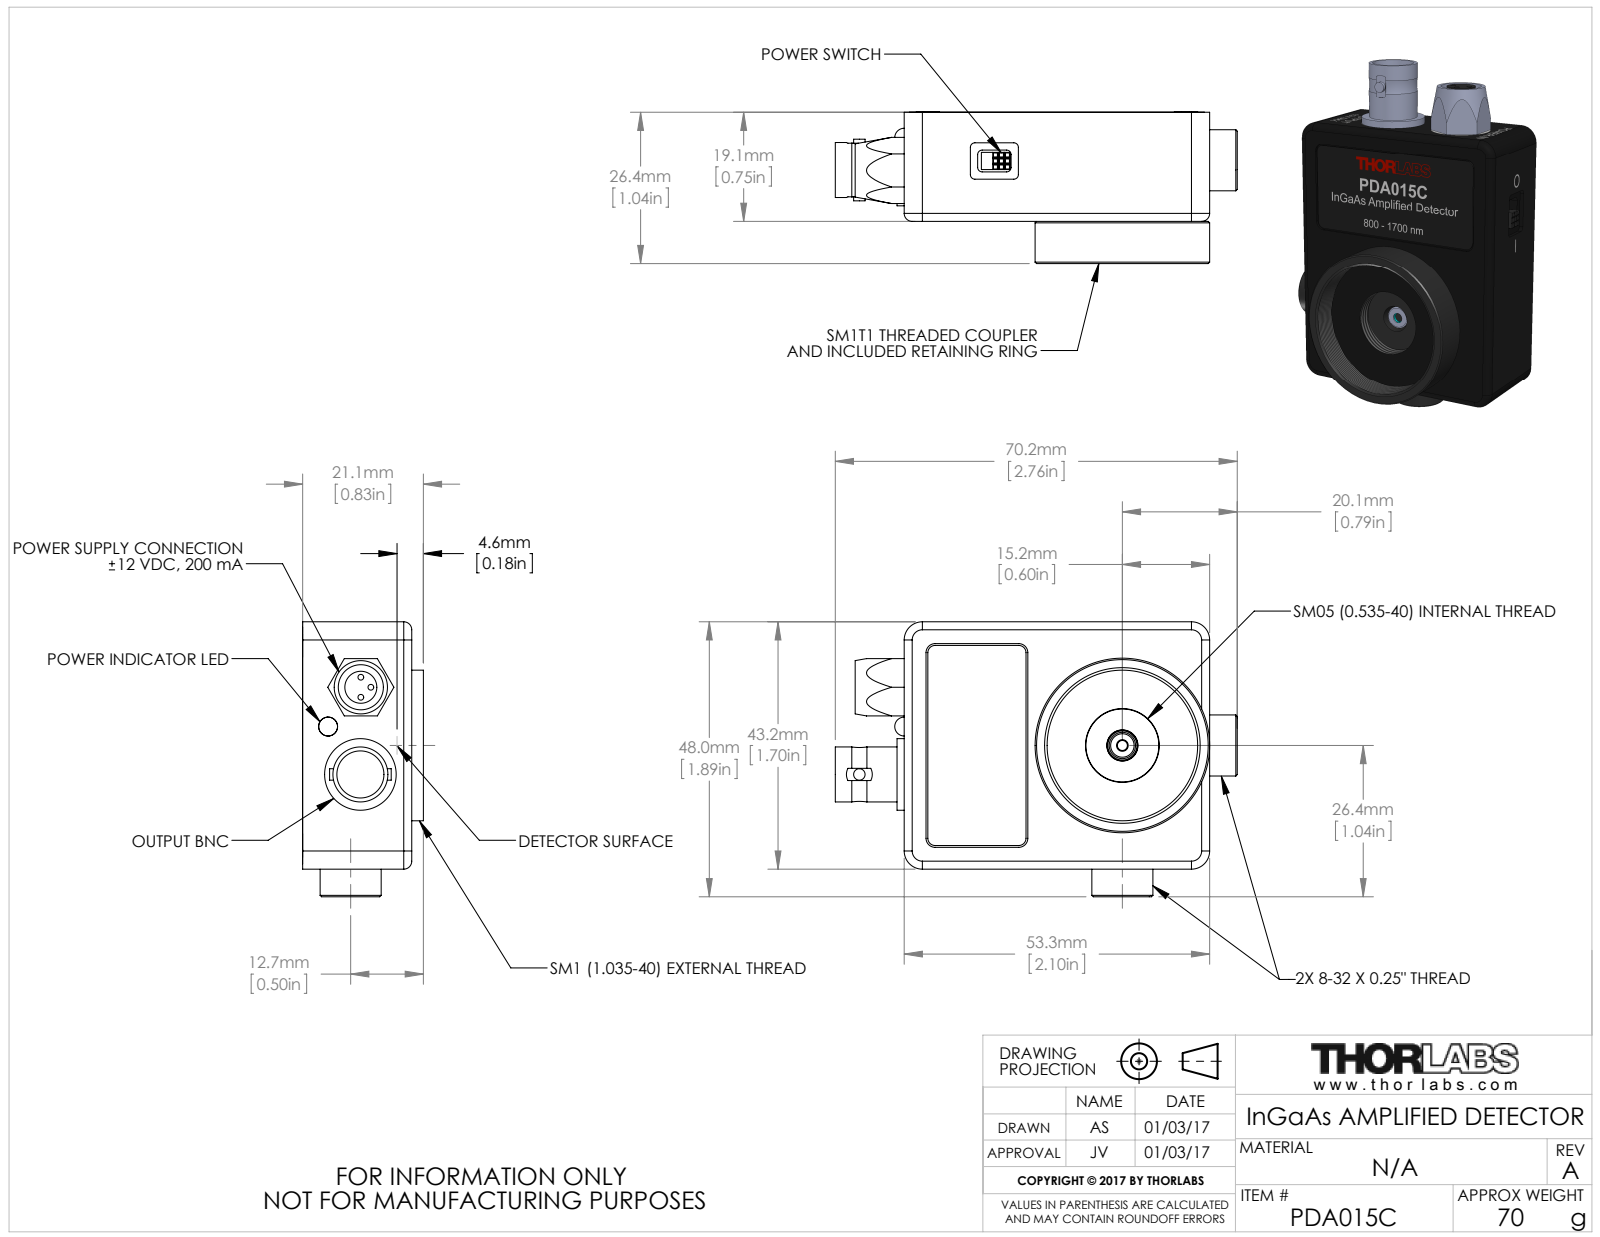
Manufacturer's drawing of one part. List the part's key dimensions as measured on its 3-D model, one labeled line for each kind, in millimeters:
Part name (STEP PRODUCT): PDA015C
STEP written by: SolidWorks 2014 (AUTOMOTIVE_DESIGN)
Units: millimetres
Bodies: 0 solids, 326 faces (199 planar, 77 cylindrical, 50 other)
Overall size (bounding box): 70.19 × 48 × 26.43
Round holes (diameter × count): ⌀1 ×3, ⌀3.45 ×2, ⌀1.75 ×1, ⌀2.03 ×1, ⌀5.44 ×1, ⌀7.87 ×1, ⌀8.22 ×1, ⌀12.88 ×1, ⌀26.29 ×1
Round bosses / shafts (diameter × count): ⌀10.66 ×2, ⌀30.48 ×1, ⌀12.5 ×1, ⌀9.6 ×1, ⌀5.59 ×1, ⌀2 ×1
Partial cylindrical surfaces — rounded edges, fillets, slot ends (radius × count): R0.79 ×7, R1.27 ×4, R1.4 ×4, R2.41 ×4, R2.54 ×4, R3.17 ×4, R1.59 ×2, R1.59 ×2
Main face-to-face distances: 19.07, 43.18, 18.56, 0.51, 18.86, 53.34, 21.1, 2.54, 2.24, 2.03
Hole centre spacings: 1.75, 2.47, 3.5, 5.34, 8.6, 10.31, 10.76, 12.04
